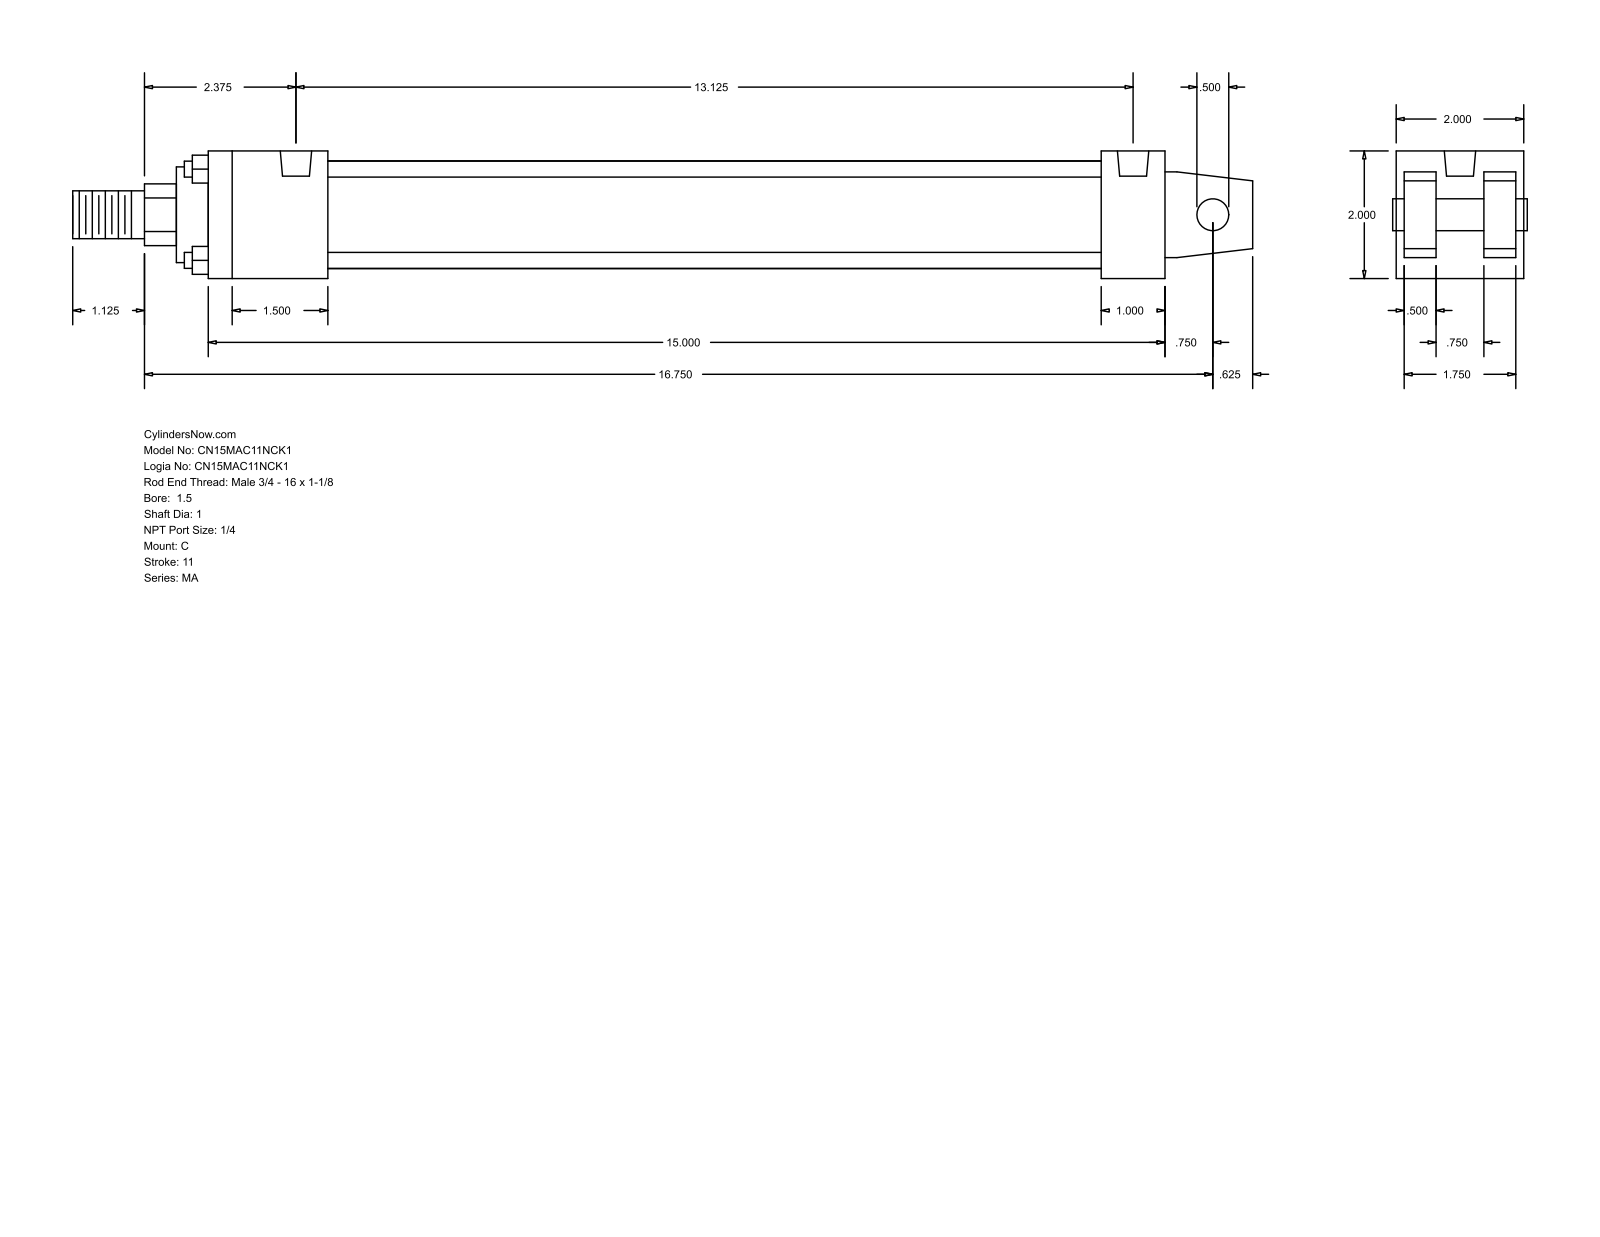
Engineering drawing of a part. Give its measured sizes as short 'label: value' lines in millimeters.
name: MA_C__0150_1
written by: GSSL Pune (CONFIG_CONTROL_DESIGN)
unit: mm
bodies: 0 solids, 103 faces (76 planar, 27 cylindrical, 0 other)
size: 469.9 × 50.8 × 50.8
holes: 4× ⌀7.94, 2× ⌀12.49
bosses: 4× ⌀6.35, 1× ⌀42.93, 1× ⌀38.1, 1× ⌀25.4, 1× ⌀19.05, 1× ⌀12.7
rounds: 1× R12.29
face distances: 50.8, 47.63, 12.7, 3.17, 15.87, 34.93, 31.76, 381, 25.4, 355.6
hole spacings: 333.37
